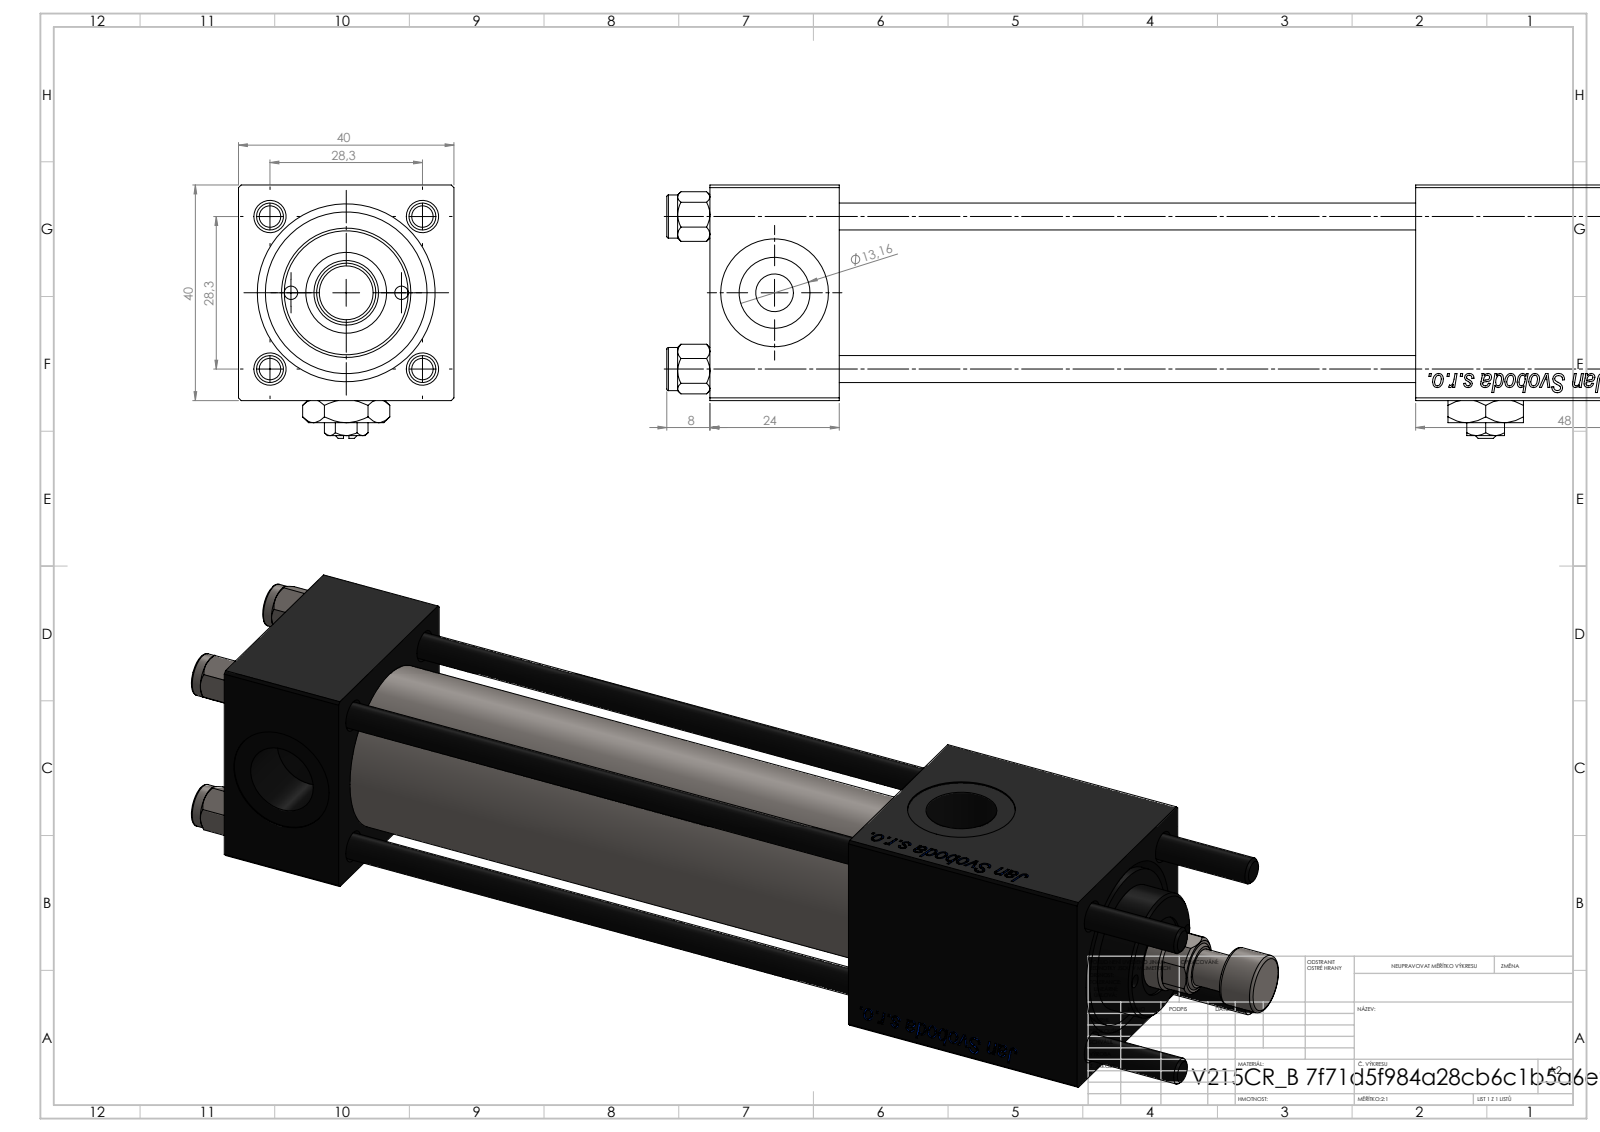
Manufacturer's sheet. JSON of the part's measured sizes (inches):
{"part_name": "Zatka_pro_OIL_PORT; NUT_M5_B; V215CR_VCP_B; V215CR_B_TYCINKA (+3 more)", "step_written_by": "SolidWorks 2019 (CONFIG_CONTROL_DESIGN)", "units": "inches", "bodies": {"solids": 13, "faces": 1223, "planar": 459, "cylindrical": 90, "other": 674}, "overall_size": [8.504, 1.85, 1.575], "volume_in3": 10.52, "surface_area_in2": 119, "round_holes": [[0.197, 4], [0.787, 4], [0.518, 3], [0.098, 2], [0.276, 2], [0.256, 1], [0.472, 1], [0.591, 1], [0.984, 1], [1.181, 1]], "round_bosses_or_shafts": [[0.315, 4], [1.22, 1], [0.945, 1], [0.433, 1]], "face_to_face_distances": [1.575, 0.945, 5.917, 4.972, 0.76, 5.157, 4.213, 7.047, 6.102, 1.89], "hole_center_spacings": [0.578, 0.788, 1.111, 1.114, 0.404, 1.576, 0.807]}
